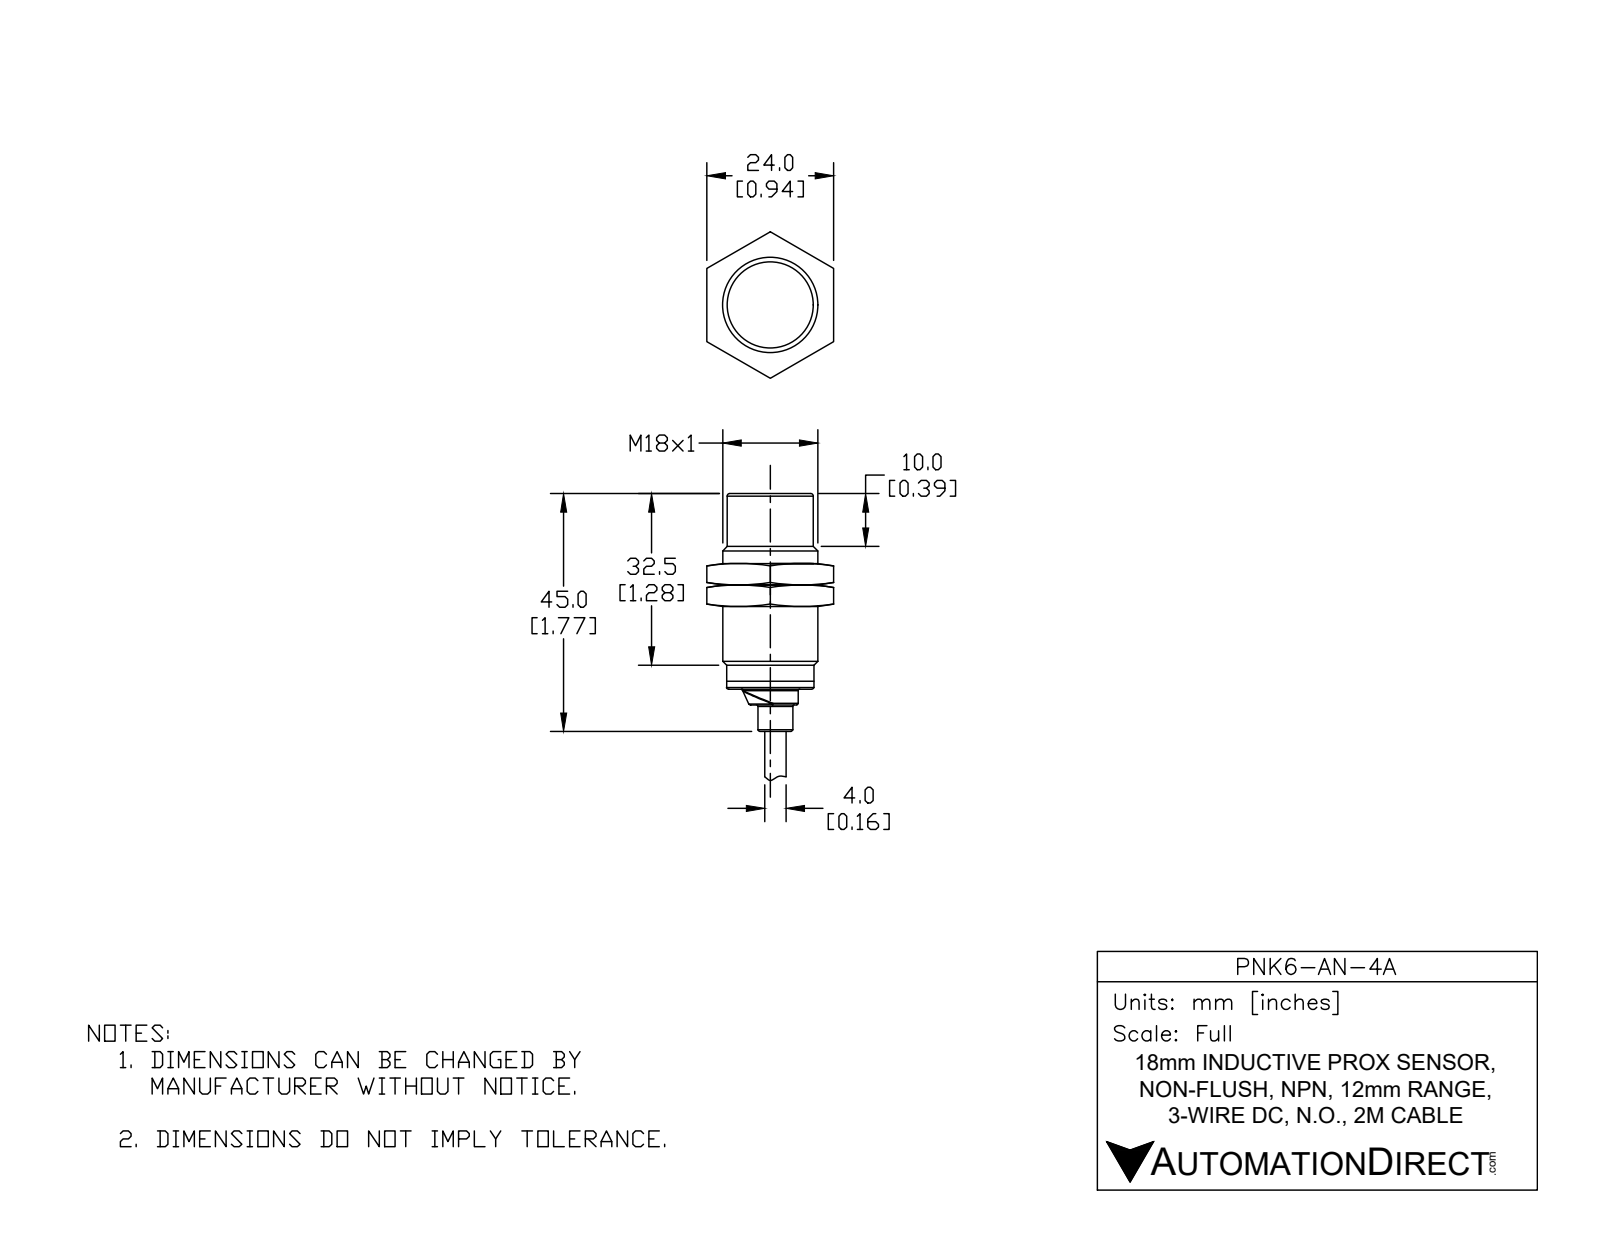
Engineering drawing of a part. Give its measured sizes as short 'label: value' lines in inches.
name: PNK6-AN-4A
written by: SolidWorks 2017 (AUTOMOTIVE_DESIGN)
unit: in
bodies: 1 solid, 78 faces (19 planar, 27 cylindrical, 32 other)
size: 3.272 × 0.709 × 0.709
volume: 0.61 in³; area: 5.425 in²
holes: 1× ⌀0.162
bosses: 6× ⌀0.049, 1× ⌀0.709, 1× ⌀0.65, 1× ⌀0.65, 1× ⌀0.417, 1× ⌀0.26, 1× ⌀0.157
rounds: 1× R0.146
face distances: 1.457, 1.398, 0.059, 1.575, 0.177, 0.118, 1.545, 0.148, 0.089, 0.03
